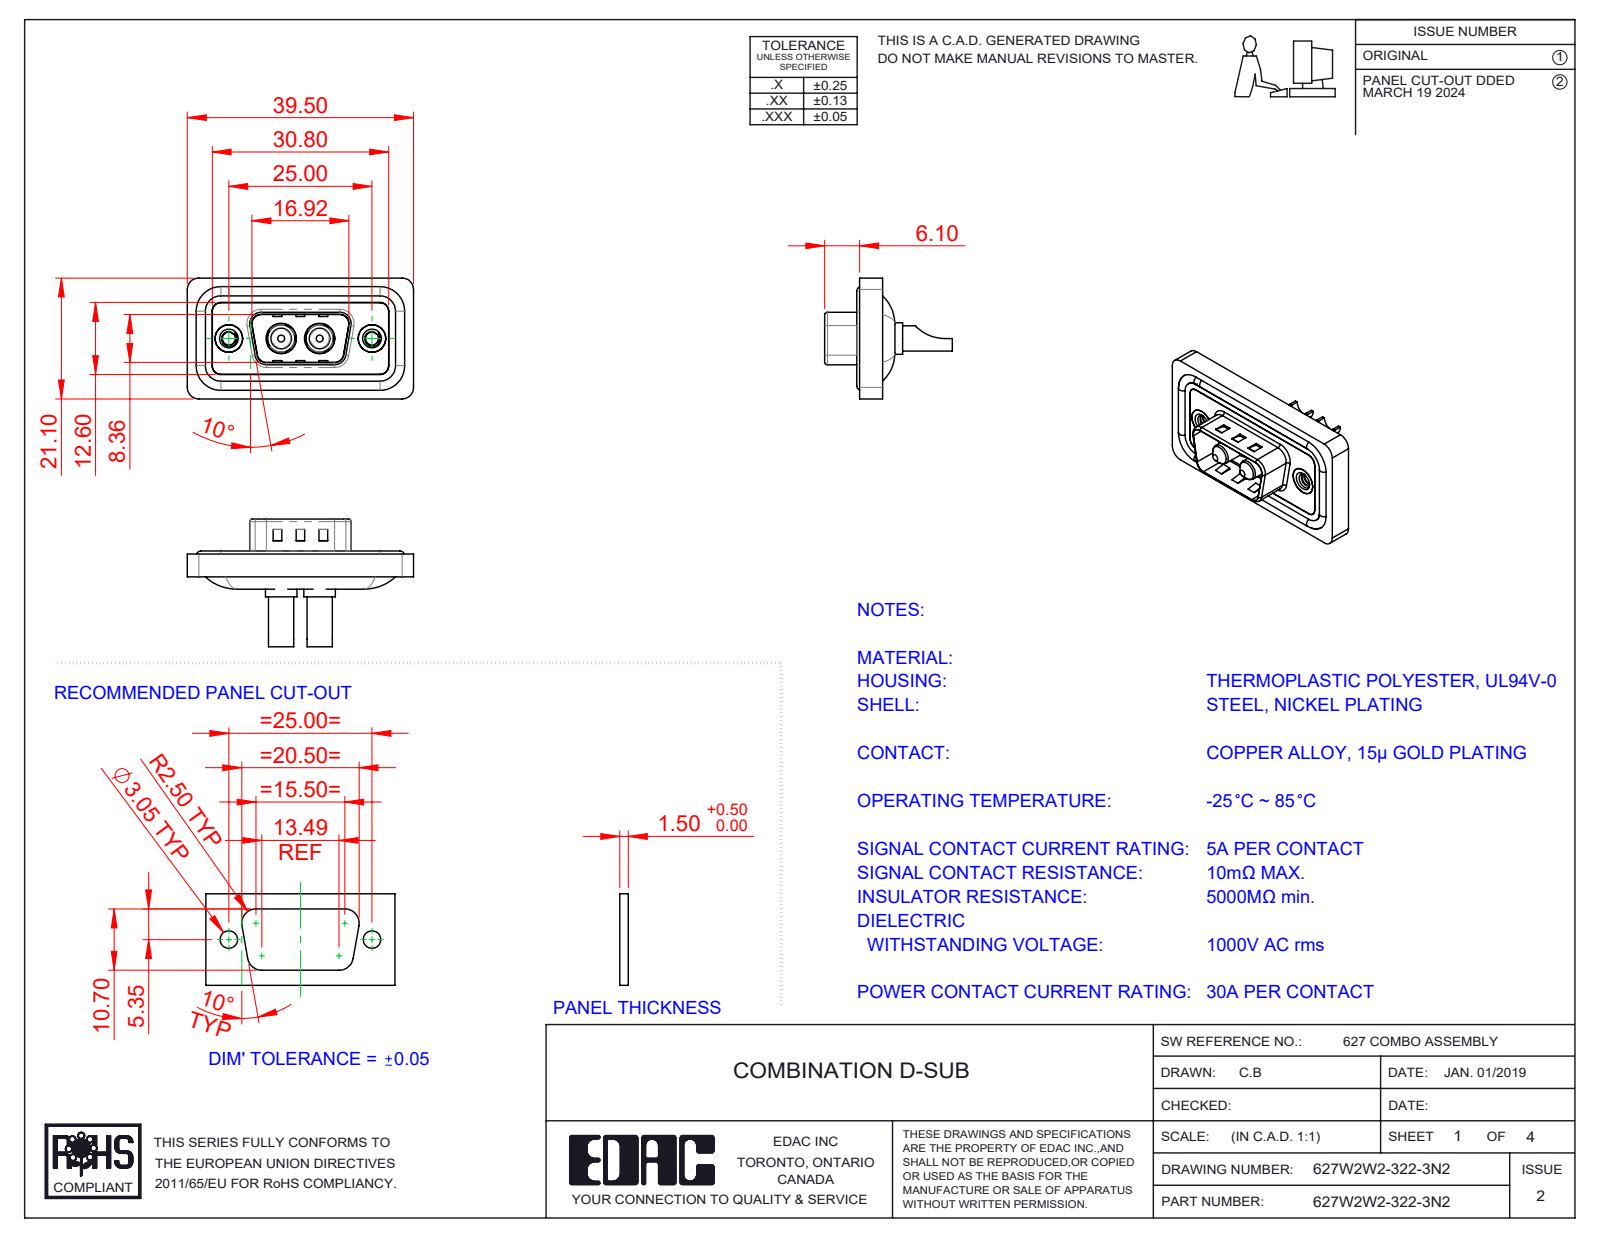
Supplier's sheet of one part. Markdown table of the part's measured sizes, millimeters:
| quantity | value |
| --- | --- |
| part name | 627Combo Housing_2W2; 627Combo Threaded Rivet_2; 627Combo Shell Front_09 Contacts; 627W2W2-322-3N2 (+3 more) |
| STEP written by | SolidWorks 2023 (CONFIG_CONTROL_DESIGN) |
| units | millimeters |
| bodies | 11 solids, 501 faces (171 planar, 224 cylindrical, 106 other) |
| overall size | 39.5 × 22.3 × 21.1 |
| volume | 4 509 mm³ |
| surface area | 7 199 mm² |
| round holes (diameter × count) | 2.26 × 2, 3.5 × 2, 4 × 2, 4.8 × 2, 4.85 × 2, 5 × 2, 5.3 × 2 |
| round bosses / shafts (diameter × count) | 1.6 × 4, 5.5 × 2, 5.2 × 2, 4.9 × 2, 4.75 × 2, 4.4 × 2, 3.75 × 2, 3.6 × 2 |
| partial cylindrical surfaces (radius × count) | 1.5 × 22, 2 × 18, 0.5 × 8, 1.6 × 8, 0.25 × 4, 0.6 × 4, 0.65 × 4, 0.9 × 4 |
| main face-to-face distances | 0.4, 1.1, 2.9, 3.1, 0.5, 1.6, 1.5, 2.5, 4, 0.7 |
| hole center spacings | 9.14, 15.86, 6.72, 25 |
